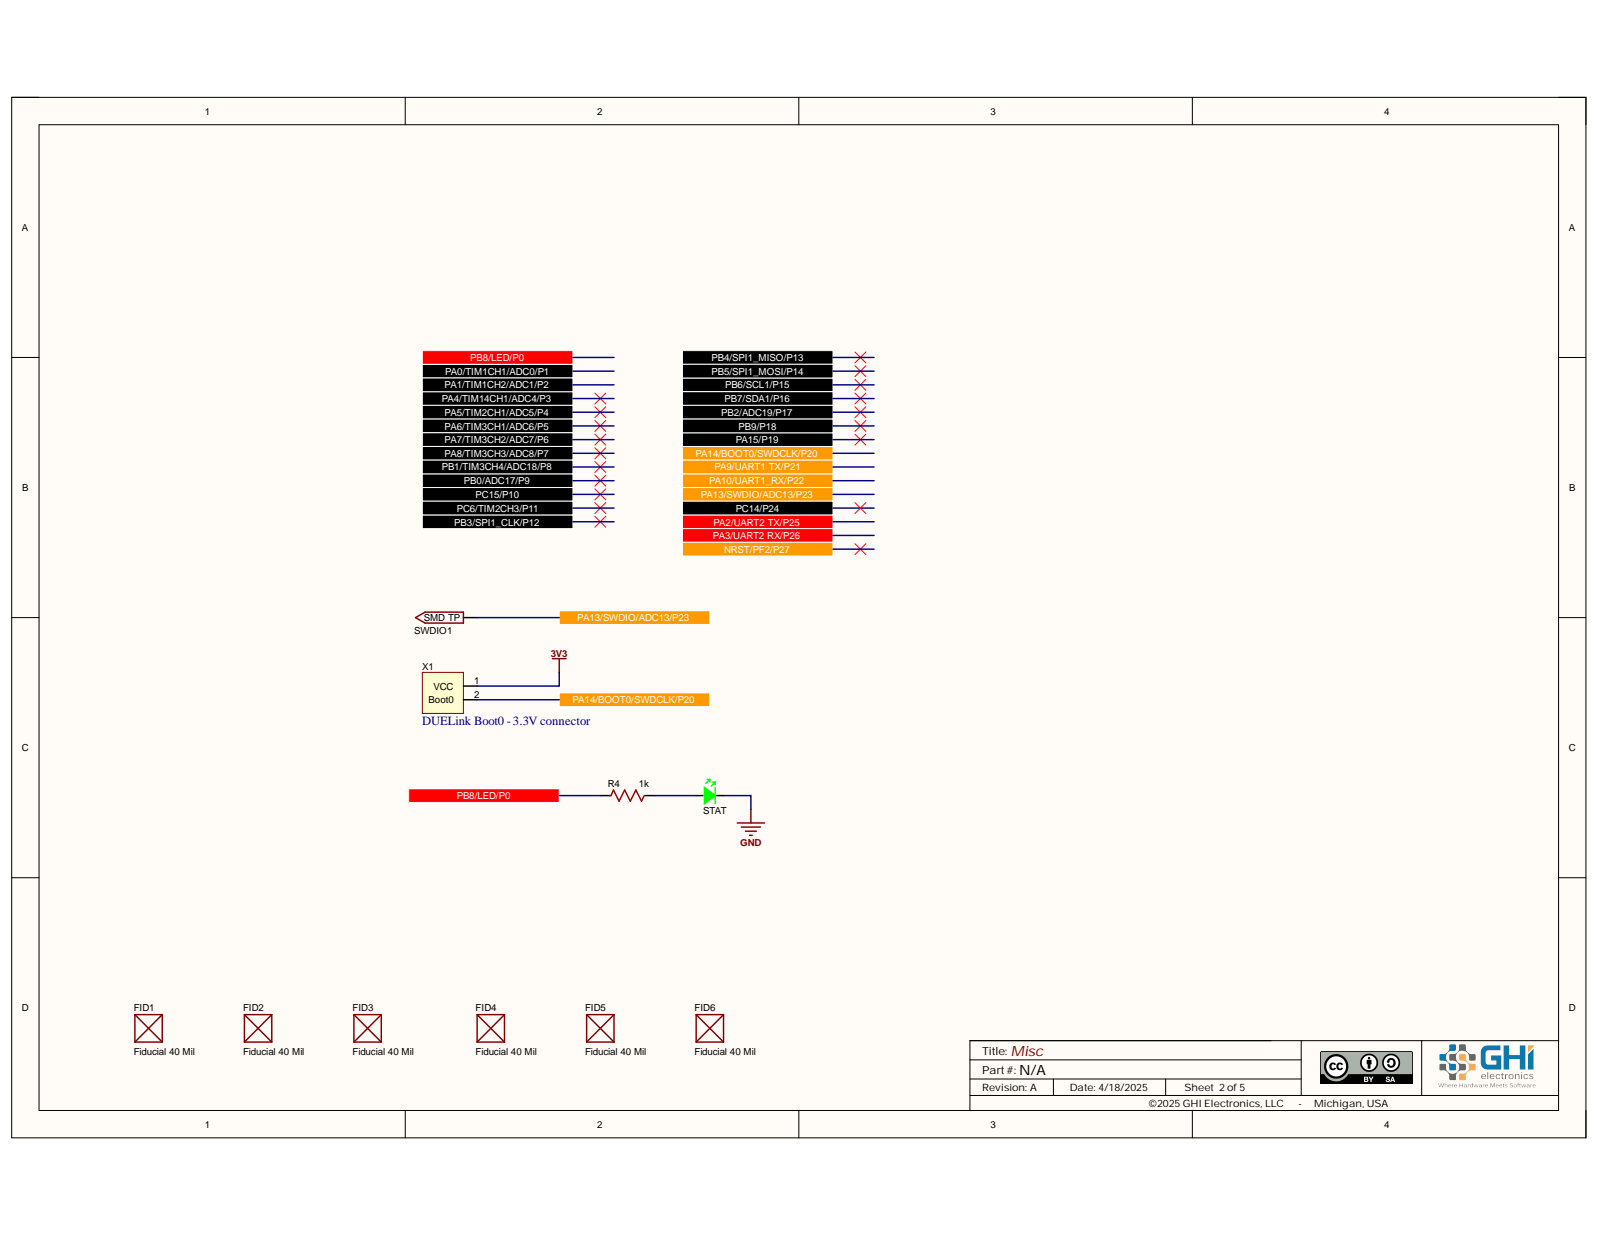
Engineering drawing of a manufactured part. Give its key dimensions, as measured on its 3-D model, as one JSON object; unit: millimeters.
{"part_name": "PCB; Board; 6300167920; Cylinder (+6 more)", "step_written_by": "Open CASCADE 7.5 (AUTOMOTIVE_DESIGN)", "units": "millimeters", "bodies": {"solids": 84, "faces": 1283, "planar": 973, "cylindrical": 210, "other": 100}, "overall_size": [27, 24.2, 9.62], "volume_mm3": 711, "surface_area_mm2": 2188, "round_holes": [[3, 4], [1.02, 2], [1.6, 2]], "round_bosses_or_shafts": [[1.5, 2], [5, 1], [3.6, 1]], "partial_cylinders_radius": [[0.12, 35], [0.15, 14], [3.5, 4], [0.17, 2], [0.18, 2], [0.18, 2]], "face_to_face_distances": [5, 5.2, 6, 1, 1.15, 0.37, 0.45, 2.53, 23.12, 9.95], "hole_center_spacings": [10, 12.38, 12.62, 15, 17.78, 20, 25, 2.54]}
